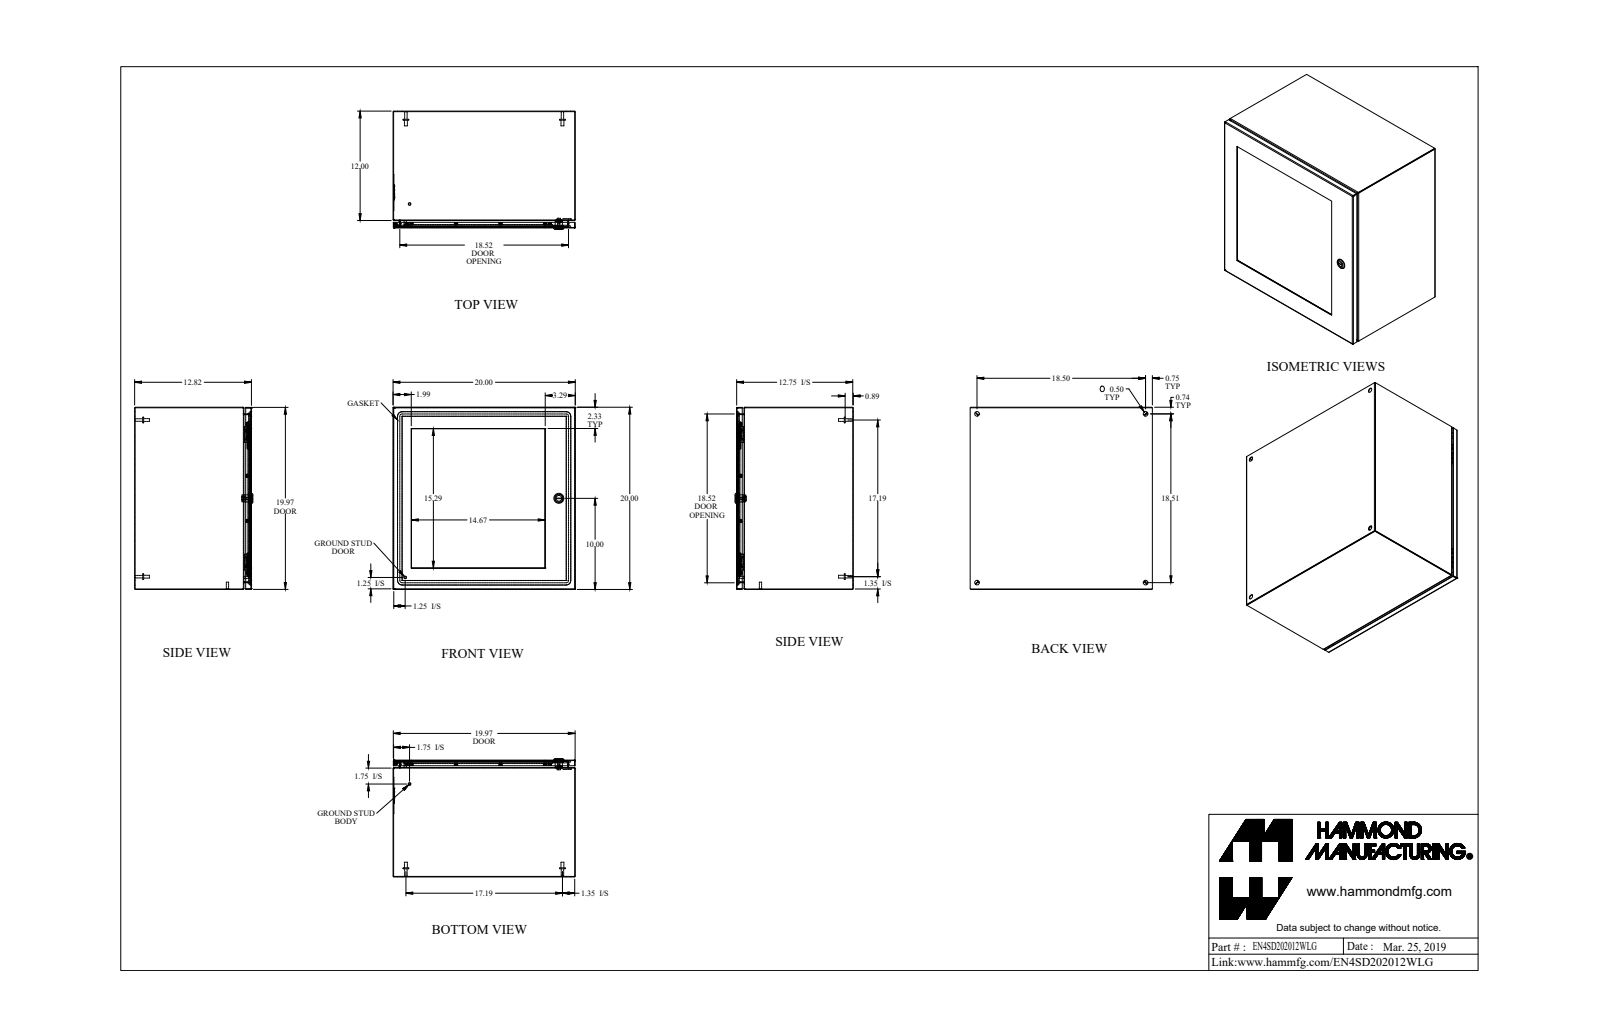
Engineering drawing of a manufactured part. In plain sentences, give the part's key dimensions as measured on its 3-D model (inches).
The part is named "EN4SD202012WLG_Default". Its 3-D file was written by "SolidWorks 2019 (CONFIG_CONTROL_DESIGN)". It is 66 solids with 1303 faces: 664 planar, 385 cylindrical and 254 other. Overall it measures 20 by 20 by 12.982 inches. Its volume is 170.1 cubic inches and its surface area 4 260 square inches. Round holes: 16 of diameter 0.13, 16 of diameter 0.25, 4 of diameter 0.5, 1 of diameter 0.172, 1 of diameter 0.232, 1 of diameter 0.24, 1 of diameter 0.242, 1 of diameter 0.625, 1 of diameter 0.785. Round bosses or shafts: 17 of diameter 0.226, 16 of diameter 0.368, 16 of diameter 0.164, 4 of diameter 0.625, 4 of diameter 0.313, 4 of diameter 0.27, 2 of diameter 0.281, 2 of diameter 0.25. Partial cylindrical surfaces (rounded edges, fillets, slot ends): 19 of radius 0.029, 19 of radius 0.086, 12 of radius 0.188, 10 of radius 0.125, 4 of radius 0.006, 4 of radius 0.016, 4 of radius 0.062, 4 of radius 0.088. The main face-to-face distances are 0.057, 19.943, 12.765, 19.886, 20, 12.708, 0.25, 12.458, 12.515, 0.307. The hole center spacings are 4.958, 9.917, 15.612, 4.959, 9.917, 14.875, 16.471, 16.475.
